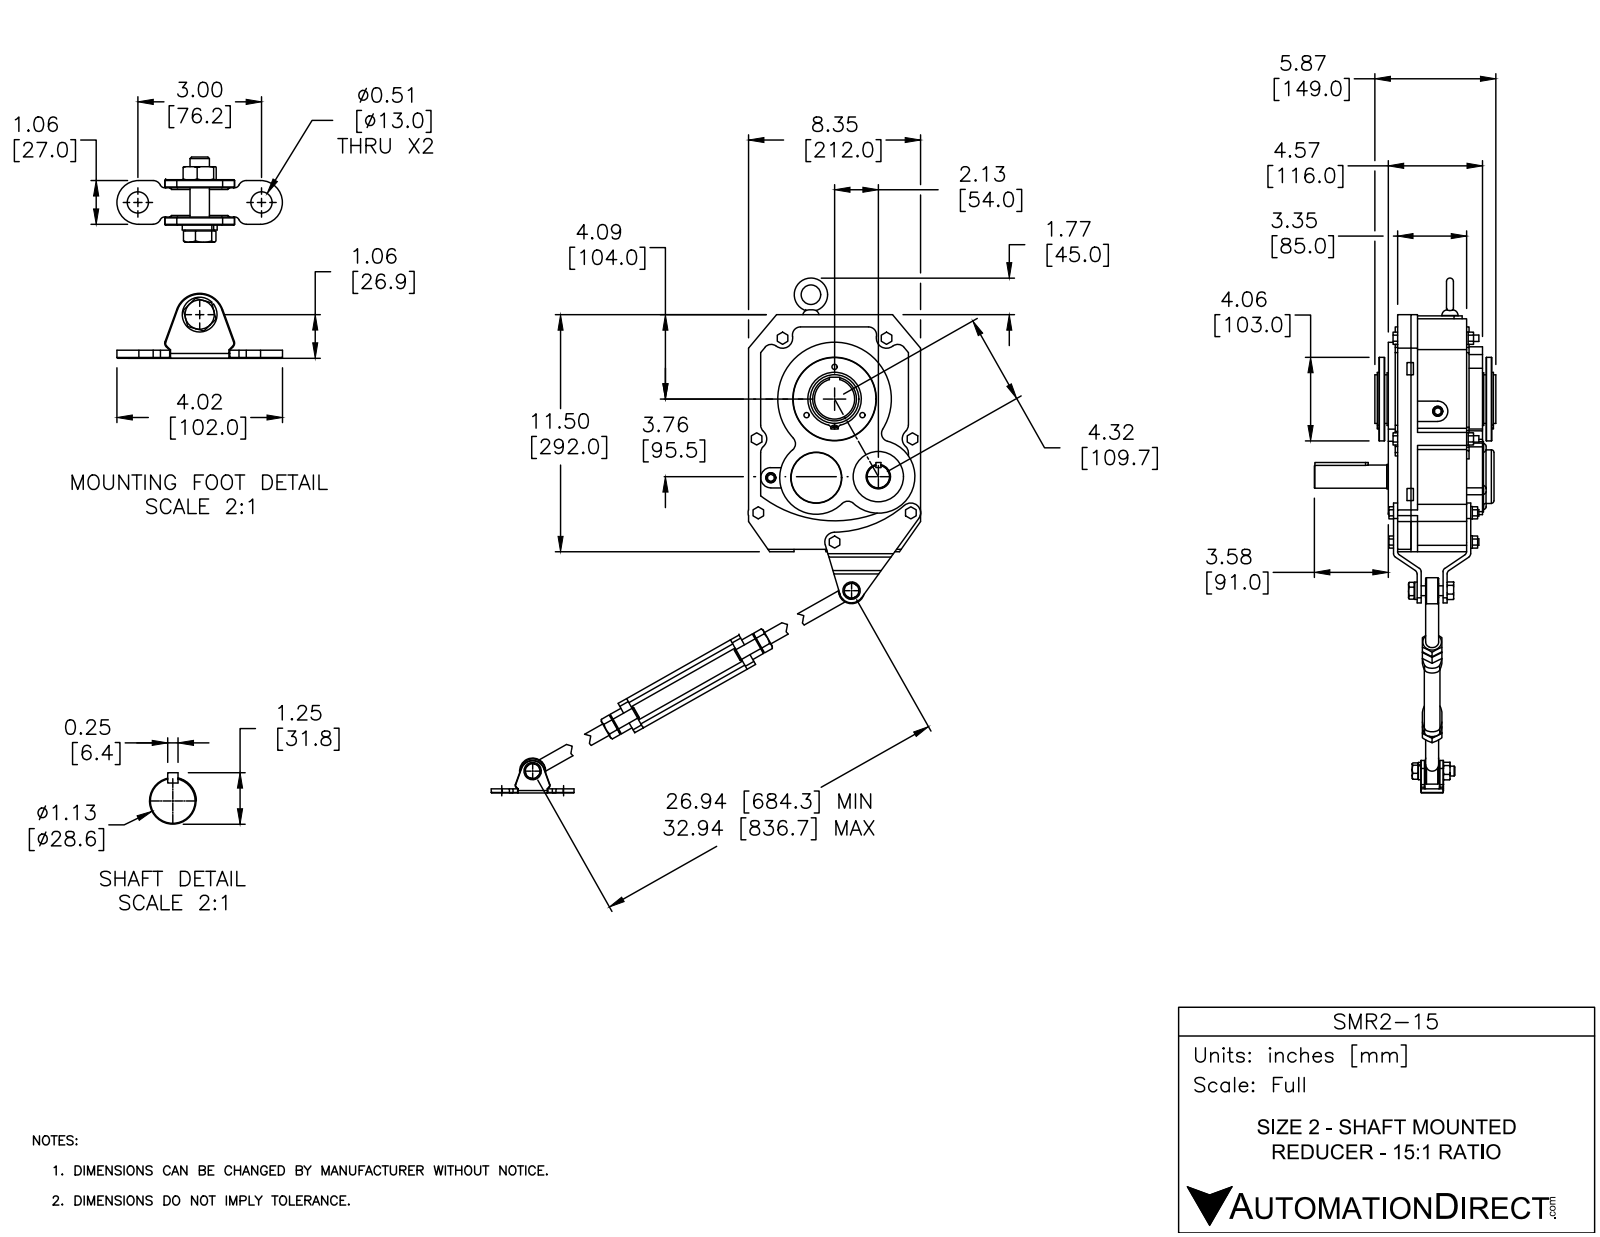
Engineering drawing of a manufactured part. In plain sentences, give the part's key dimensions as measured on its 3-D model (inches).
The part is named "SMR2-15; SMR2-TA; SMR2-TA_5; SMR2-TA_4 (+4 more)". Its 3-D file was written by "SolidWorks 2016 (AUTOMOTIVE_DESIGN)". It is 58 solids with 1229 faces: 599 planar, 435 cylindrical and 195 other. Overall it measures 32.574 by 31.591 by 8.799 inches. Its volume is 364 cubic inches and its surface area 1 056 square inches. Round holes: 8 of diameter 0.313, 7 of diameter 0.315, 7 of diameter 0.374, 3 of diameter 0.256, 3 of diameter 0.472, 3 of diameter 0.484, 3 of diameter 0.512, 2 of diameter 0.098, 2 of diameter 0.48, 2 of diameter 0.508, 2 of diameter 0.63, 1 of diameter 0.551. Round bosses or shafts: 7 of diameter 0.606, 4 of diameter 0.413, 3 of diameter 0.472, 2 of diameter 1.26, 2 of diameter 0.878, 2 of diameter 0.846, 2 of diameter 0.709, 2 of diameter 0.63. Partial cylindrical surfaces (rounded edges, fillets, slot ends): 22 of radius 0.02, 19 of radius 0.394, 16 of radius 0.197, 8 of radius 0.118, 8 of radius 0.492, 4 of radius 0.079, 3 of radius 0.236, 2 of radius 0.039. The main face-to-face distances are 3.465, 0.65, 0.768, 0.453, 0.197, 1.102, 0.118, 4.567, 3.799, 3.346. The hole center spacings are 2.5, 3.535, 1.563, 2.707, 1.07, 1.336, 1.378, 1.38.
